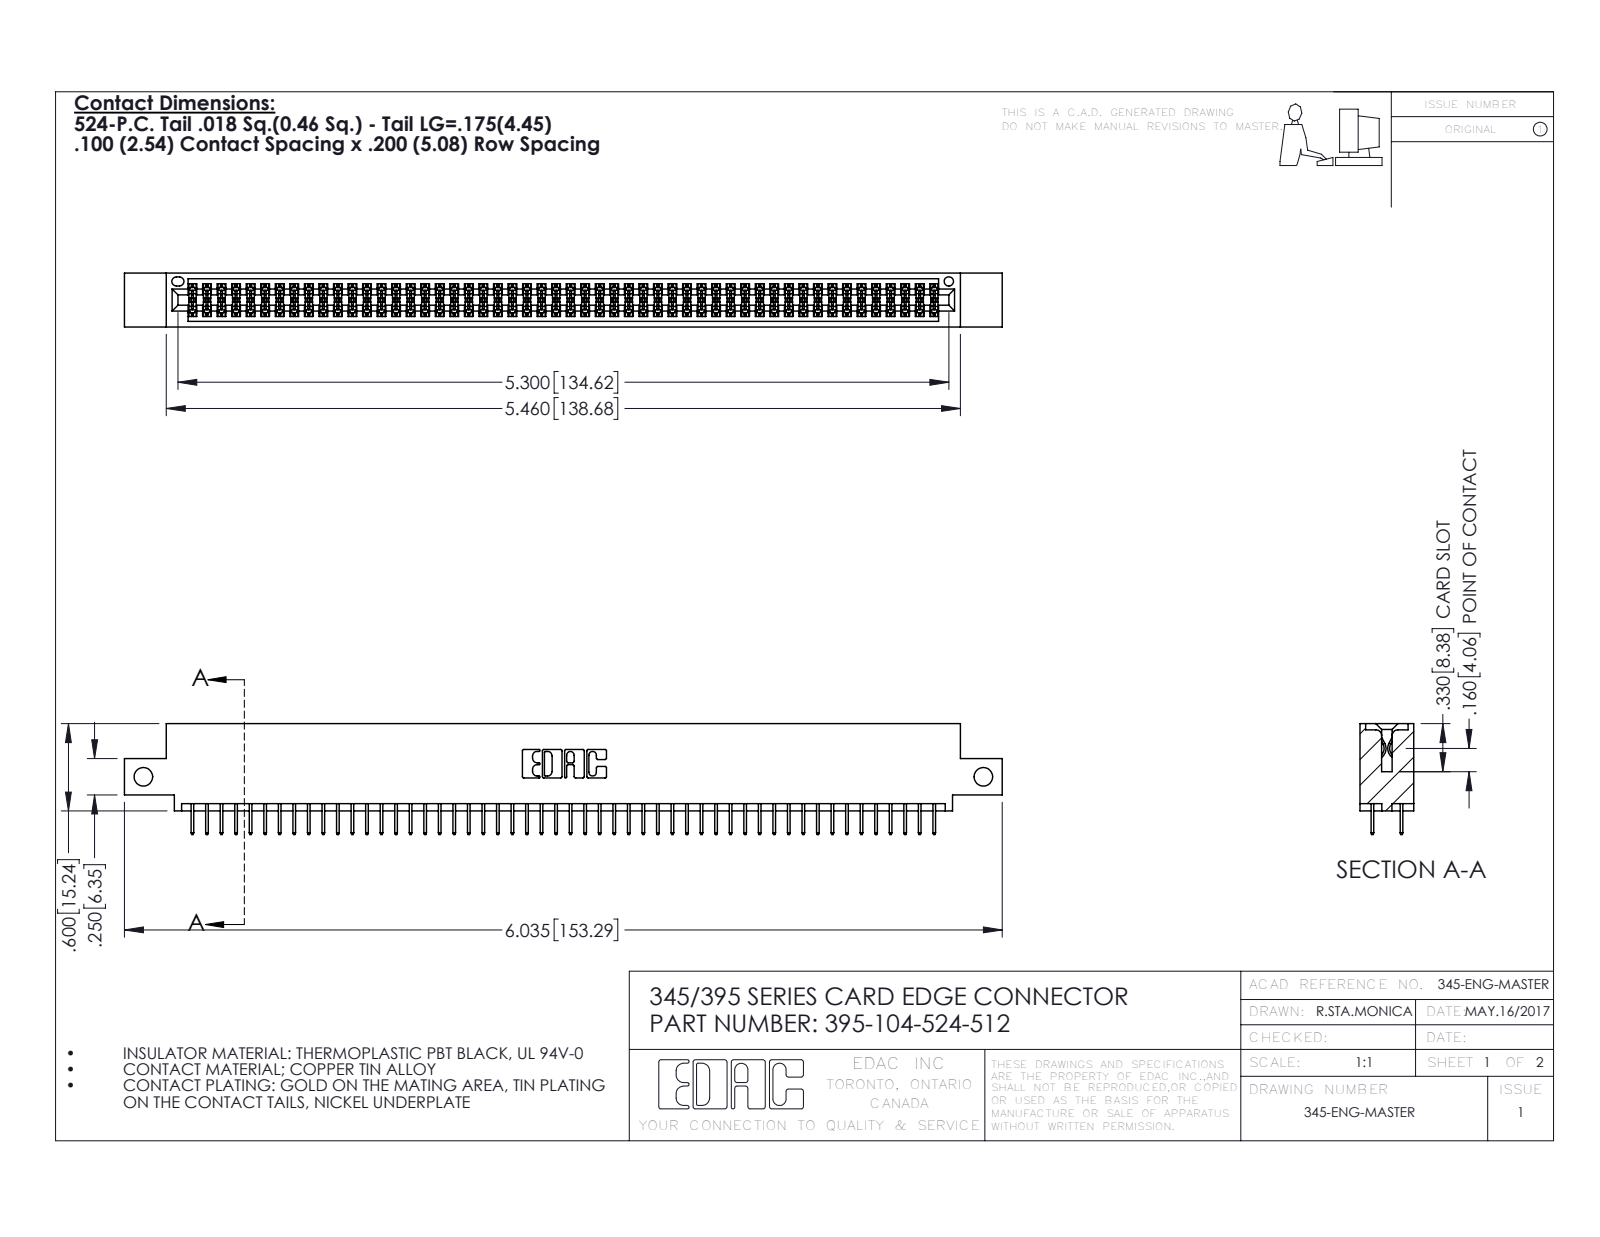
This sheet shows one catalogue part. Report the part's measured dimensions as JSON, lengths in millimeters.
{"part_name": "345 Part_0.110 Offset - Side Mount; 395-104-524-512; 345-292-001_345-293-124", "step_written_by": "SolidWorks 2016 (CONFIG_CONTROL_DESIGN)", "units": "millimeters", "bodies": {"solids": 105, "faces": 5746, "planar": 4140, "cylindrical": 1606, "other": 0}, "overall_size": [153.3, 19.4, 9.4], "volume_mm3": 14700, "surface_area_mm2": 21410, "round_holes": [[3.3, 2], [1.6, 1]], "partial_cylinders_radius": [[0.2, 156], [0.3, 22], [0.2, 6], [0.8, 6], [0.7, 3], [0.4, 2], [0.5, 2], [0.6, 2]], "face_to_face_distances": [1.8, 7.6, 5.1, 9.4, 2.5, 6.9, 0.6, 5.7, 1.8, 4.4], "hole_center_spacings": [146.7]}
